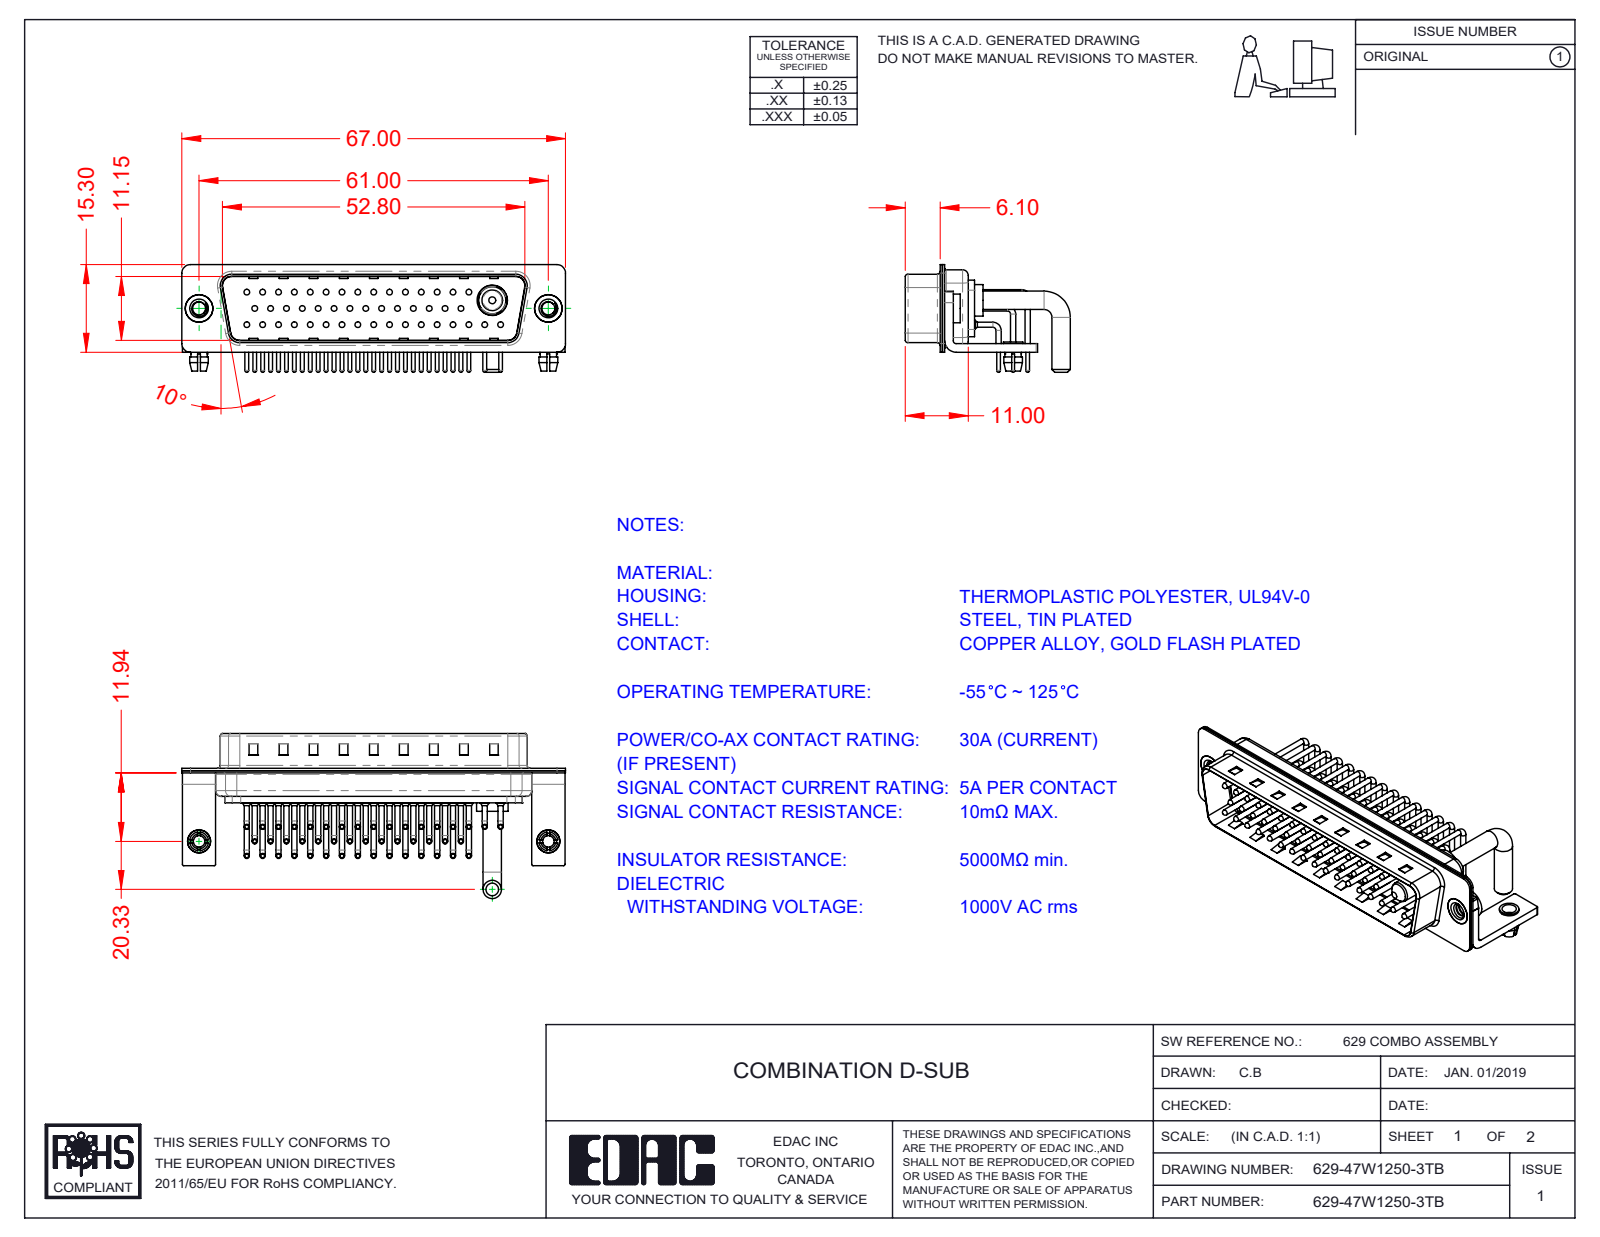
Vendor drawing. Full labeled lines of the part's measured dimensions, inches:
Part name (STEP PRODUCT): Power Pin_Ext 30A RA 50; 629Combo Contact Row 2_50 Contacts; 629Combo Board Lock_50 Contacts; 629Combo Contact Row 3 (+7 more)
STEP written by: SolidWorks 2020 (CONFIG_CONTROL_DESIGN)
Units: inches
Bodies: 57 solids, 5655 faces (3225 planar, 1874 cylindrical, 556 other)
Overall size (bounding box): 2.638 × 1.135 × 0.74
Volume: 0.343 in³ · Surface area: 21.42 in²
Round holes (diameter × count): ⌀0.079 ×48, ⌀0.03 ×46, ⌀0.063 ×46, ⌀0.089 ×2, ⌀0.098 ×2, ⌀0.126 ×2, ⌀0.157 ×2, ⌀0.189 ×2, ⌀0.191 ×1, ⌀0.209 ×1
Round bosses / shafts (diameter × count): ⌀0.035 ×92, ⌀0.059 ×46, ⌀0.039 ×46, ⌀0.026 ×46, ⌀0.197 ×2, ⌀0.193 ×2, ⌀0.157 ×2, ⌀0.134 ×2
Partial cylindrical surfaces — rounded edges, fillets, slot ends (radius × count): R0.04 ×46, R0.01 ×16, R0.059 ×16, R0.079 ×13, R0.02 ×9, R0.063 ×8, R0.024 ×4, R0.026 ×4
Main face-to-face distances: 0.016, 0.059, 0.455, 0.22, 0.205, 0.161, 0.031, 0.236, 0.075, 0.031
Hole centre spacings: 0.109, 0.124, 0.218, 0.327, 0.436, 0.545, 0.654, 0.763
